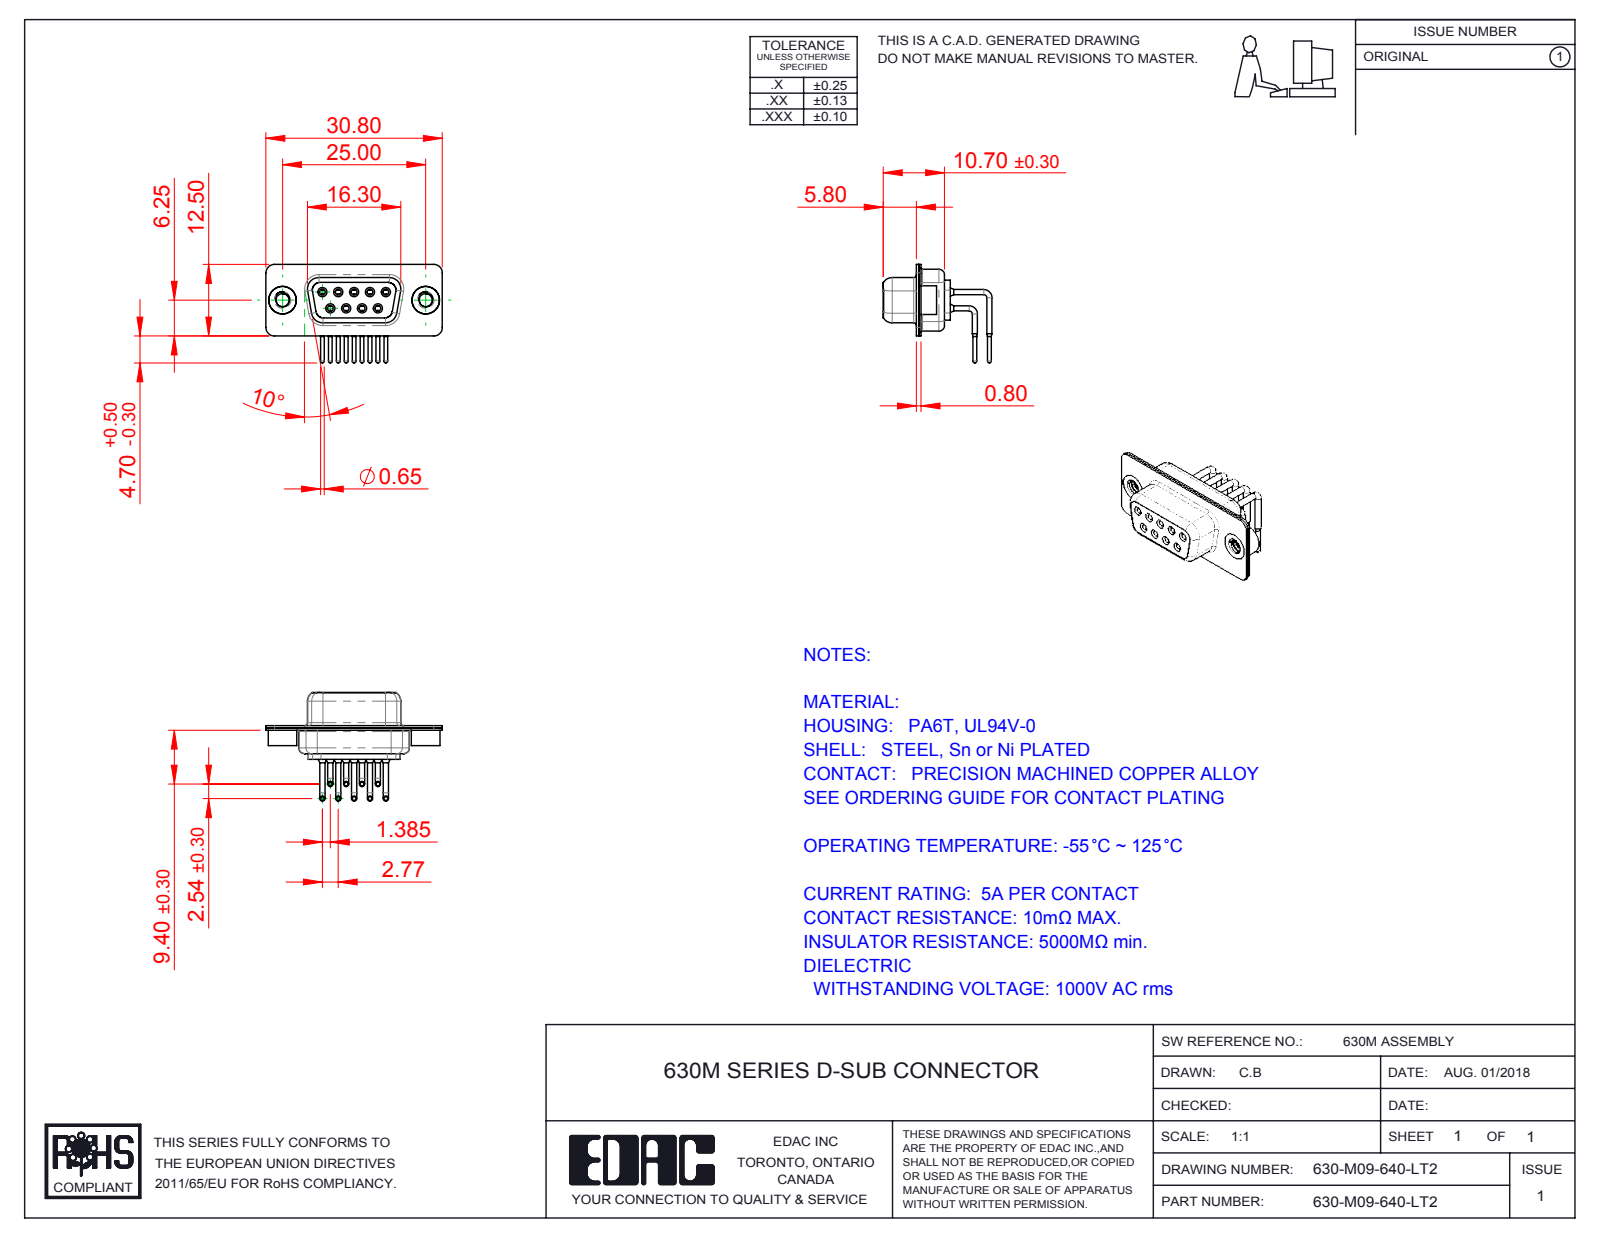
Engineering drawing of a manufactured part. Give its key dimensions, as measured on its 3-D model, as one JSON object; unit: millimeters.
{"part_name": "630M Housing_09 Contacts; 630M Shell Front_09 Contacts; 630M Contact Row 1; 630M Shell Rear_09 Contacts (+3 more)", "step_written_by": "SolidWorks 2016 (CONFIG_CONTROL_DESIGN)", "units": "millimeters", "bodies": {"solids": 14, "faces": 756, "planar": 202, "cylindrical": 344, "other": 210}, "overall_size": [30.8, 18.99, 17.2], "volume_mm3": 1761, "surface_area_mm2": 4640, "round_holes": [[1, 9], [1.1, 9], [1.7, 9], [1.8, 9], [2, 9], [2.26, 2], [4, 2], [4.8, 2]], "round_bosses_or_shafts": [[0.9, 18], [1.6, 9], [1.5, 9], [0.65, 9], [5, 2], [4.9, 2]], "partial_cylinders_radius": [[1.5, 16], [2, 12], [1.35, 8], [1.6, 8], [0.25, 4], [0.5, 4], [0.6, 4], [0.65, 4]], "face_to_face_distances": [0.4, 0.8, 1.45, 2.3, 8.95, 6.2, 8.5, 1.9, 0.85, 9.35], "hole_center_spacings": [3.16, 2.77, 5.54, 5.03, 5.04, 8.31, 7.1, 7.48]}
